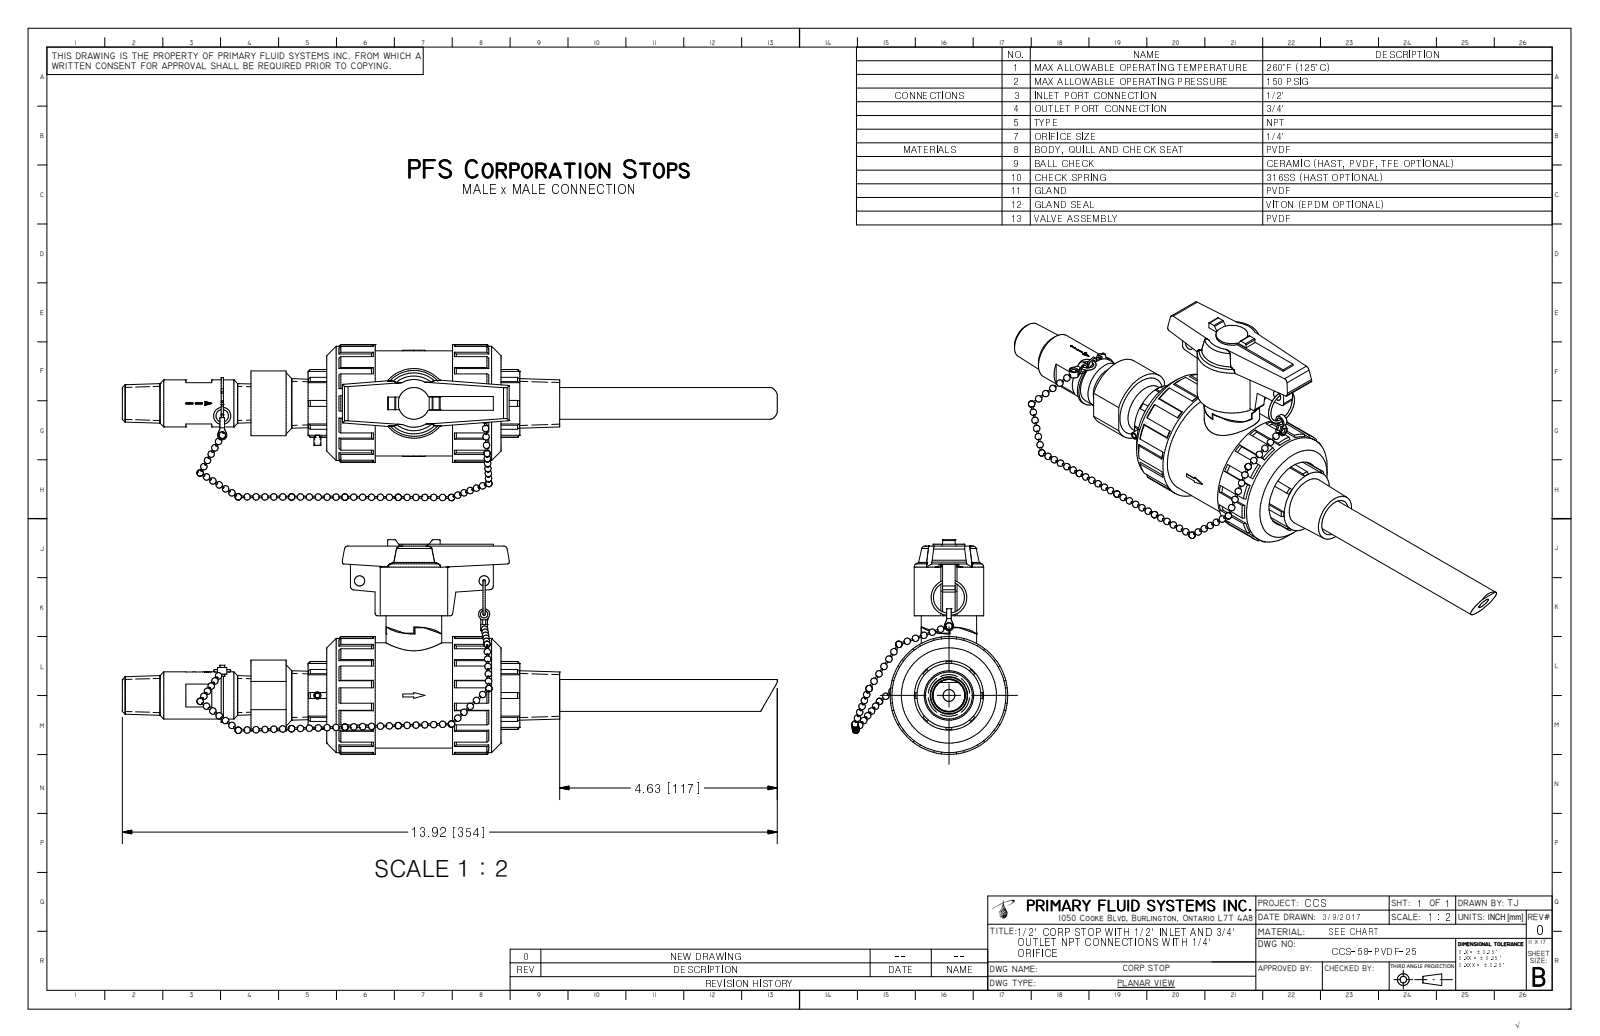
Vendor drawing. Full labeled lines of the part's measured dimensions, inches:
Part name (STEP PRODUCT): CCS-58-PVDF-25_R0
STEP written by: Autodesk Inventor 2009 (AUTOMOTIVE_DESIGN)
Units: inches
Bodies: 1 solid, 611 faces (294 planar, 77 cylindrical, 240 other)
Overall size (bounding box): 13.922 × 4.554 × 3.314
Volume: 25.84 in³ · Surface area: 123.5 in²
Round holes (diameter × count): ⌀0.079 ×1, ⌀0.217 ×1, ⌀0.25 ×1, ⌀0.469 ×1, ⌀0.56 ×1, ⌀1.47 ×1, ⌀2.16 ×1
Round bosses / shafts (diameter × count): ⌀2.5 ×1, ⌀2.422 ×1, ⌀2.232 ×1, ⌀1.801 ×1, ⌀1.476 ×1, ⌀1.36 ×1, ⌀1.181 ×1, ⌀1.18 ×1
Partial cylindrical surfaces — rounded edges, fillets, slot ends (radius × count): R0.02 ×4, R0.079 ×4, R0.039 ×2, R0.043 ×2, R0.059 ×2, R0.157 ×2, R0.337 ×1, R0.463 ×1
Main face-to-face distances: 0.039, 0.266, 0.306, 0.472, 3.233, 0.23, 3.475, 0.242, 3.003, 1.03
Hole centre spacings: 0.535
